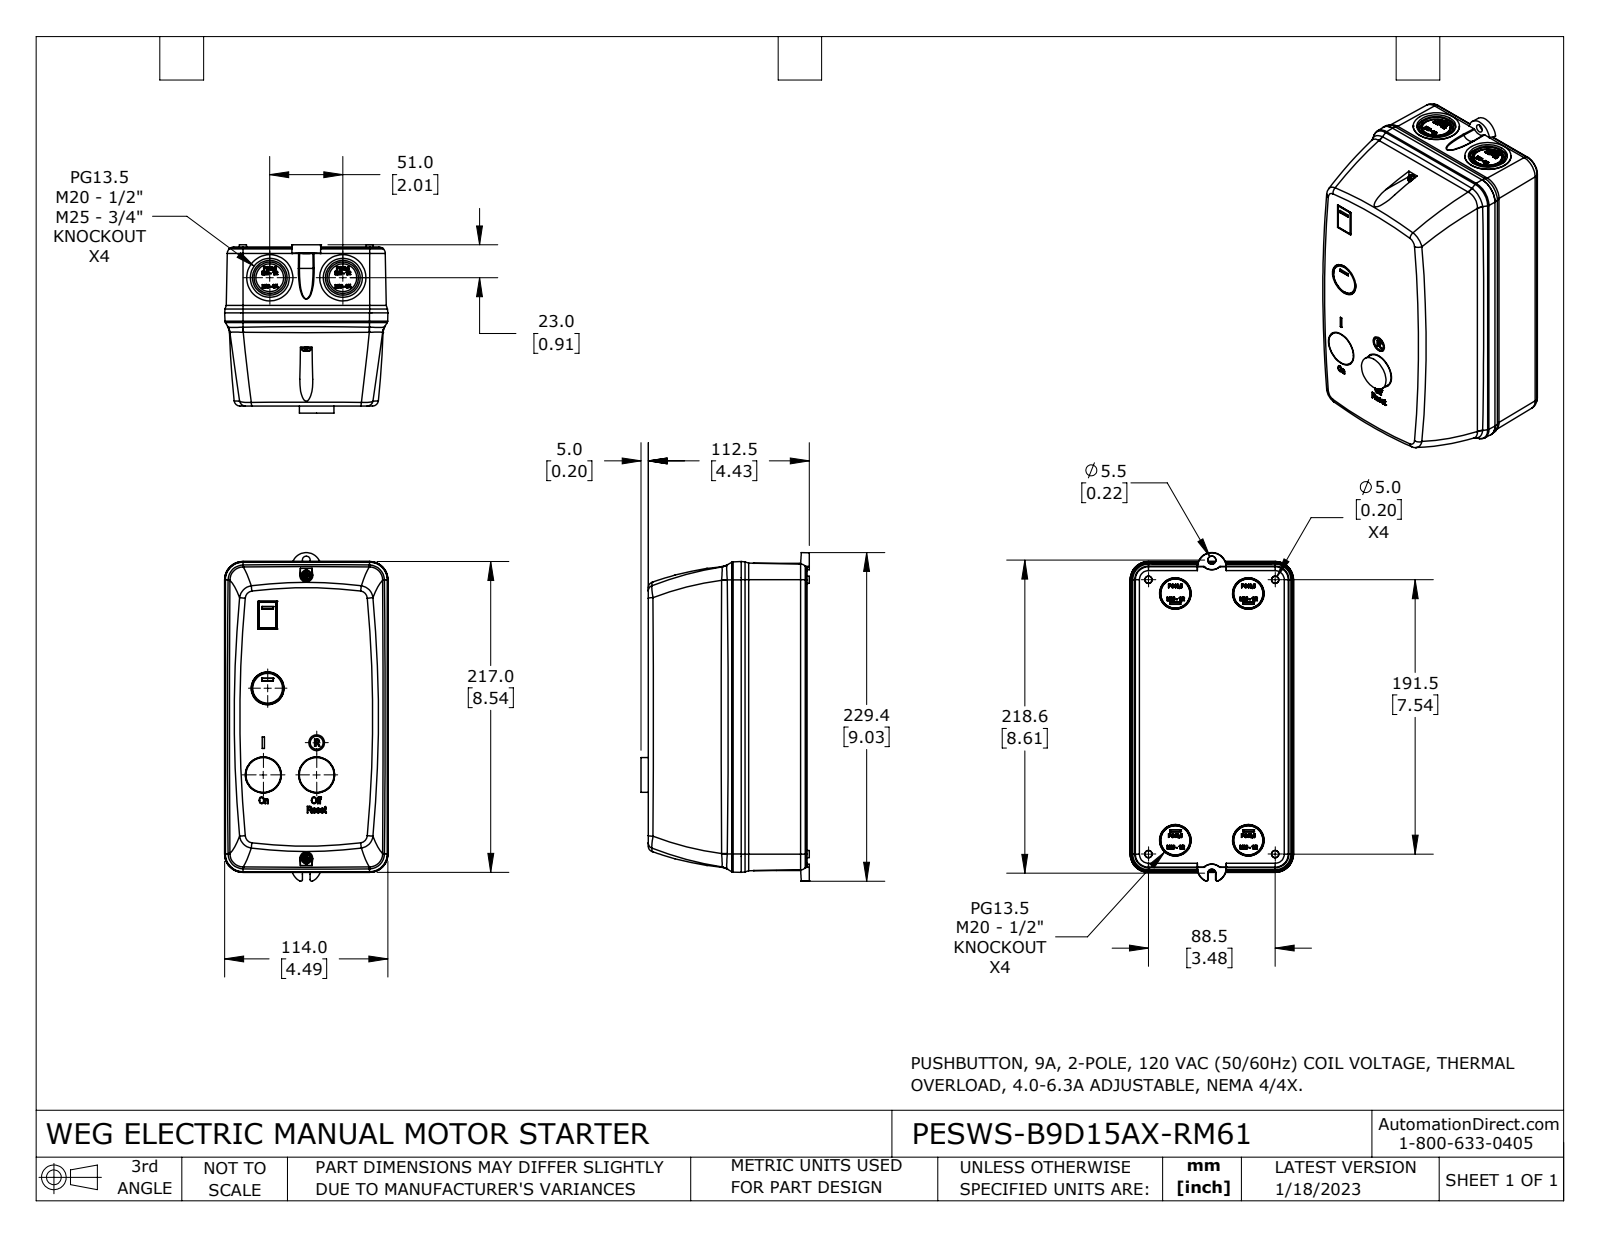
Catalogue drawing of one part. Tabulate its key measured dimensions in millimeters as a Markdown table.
| quantity | value |
| --- | --- |
| part name | PESWS-B9D15AX-RM61 |
| STEP written by | SolidWorks 2021 (CONFIG_CONTROL_DESIGN) |
| units | millimeters |
| bodies | 6 solids, 2195 faces (1110 planar, 92 cylindrical, 993 other) |
| overall size | 229.44 × 117.5 × 114.01 |
| volume | 2 457 000 mm³ |
| surface area | 166 196 mm² |
| round holes (diameter × count) | 4.4 × 2, 21.91 × 2, 27.24 × 2, 5.5 × 1, 11 × 1 |
| round bosses / shafts (diameter × count) | 32.26 × 2, 24.25 × 2, 24.2 × 2, 19.37 × 2, 7 × 2, 3 × 2, 9 × 1 |
| partial cylindrical surfaces (radius × count) | 2 × 4, 4.61 × 4, 9.54 × 4, 6.54 × 2, 7.54 × 2, 2.08 × 1, 2.17 × 1, 2.75 × 1 |
| main face-to-face distances | 46, 65, 111, 0.5, 110.5, 45.5, 110, 1, 109.5, 64 |
| hole center spacings | 10.5, 51, 81.32, 117.22, 127.71, 198, 208.5 |
